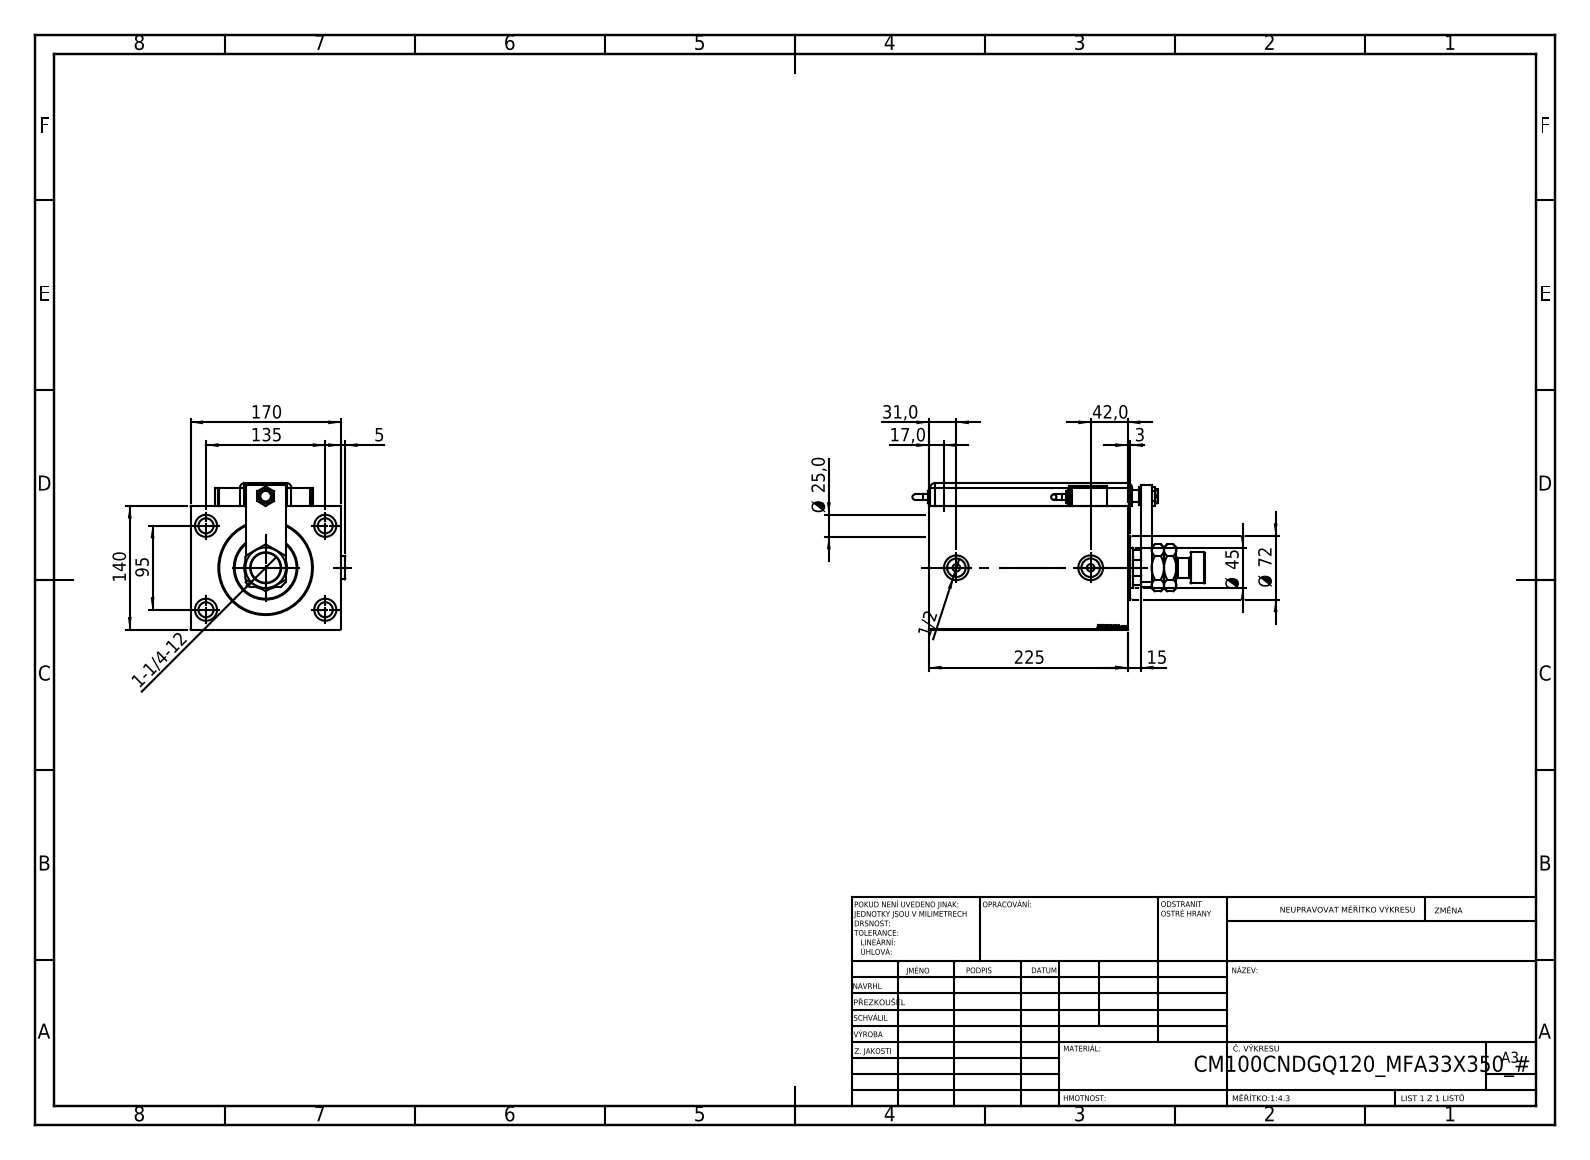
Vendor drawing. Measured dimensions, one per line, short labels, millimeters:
name: SWITCH Q; SWITCH_Q_FRONT_BACK; MAGNETIC SWITCH Q; Q_T_W_MFA (+8 more)
written by: SolidWorks 2019 (CONFIG_CONTROL_DESIGN)
unit: mm
bodies: 16 solids, 1355 faces (665 planar, 137 cylindrical, 553 other)
size: 330.76 × 174.9 × 165.8
volume: 4 649 000 mm³; area: 495 522 mm²
holes: 4× ⌀17, 4× ⌀25, 2× ⌀4, 2× ⌀8, 2× ⌀8.5, 2× ⌀20.96, 2× ⌀28, 1× ⌀12, 1× ⌀13, 1× ⌀14, 1× ⌀31.5, 1× ⌀33
bosses: 3× ⌀20, 2× ⌀26, 2× ⌀16, 2× ⌀14, 2× ⌀6, 1× ⌀72, 1× ⌀35, 1× ⌀22
rounds: 9× R5, 1× R10, 1× R22
face distances: 140, 170, 3, 225, 26, 199, 15, 25.8, 165.8, 162.8
hole spacings: 82.54, 75.36, 95, 135, 145.15, 165.08, 20, 81
